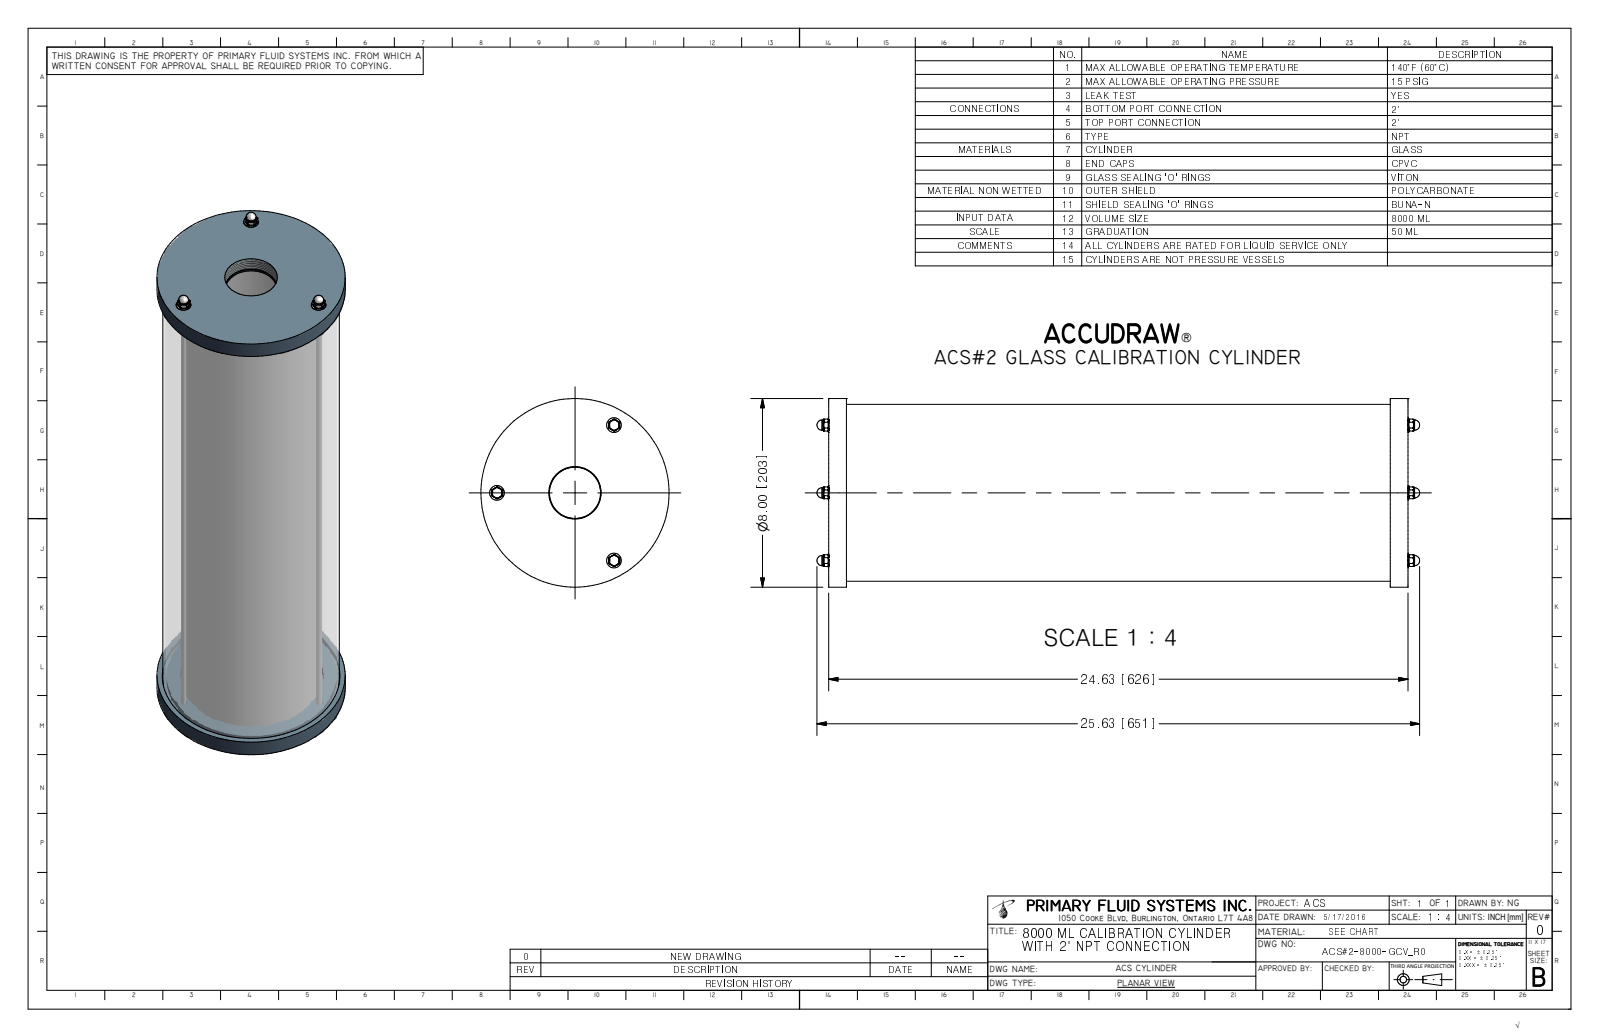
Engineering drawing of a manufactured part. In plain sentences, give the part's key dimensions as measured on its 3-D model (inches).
The part is named "ACS#2-8000-GCV_R0; ACS-3-6000-POLY_R3; ACS-2-8000_R6; ACS-1-8000-A_R0 (+3 more)". Its 3-D file was written by "Autodesk Inventor 2009 (AUTOMOTIVE_DESIGN)". It is 19 solids with 429 faces: 38 planar, 41 cylindrical and 350 other. Overall it measures 25.628 by 8 by 8 inches. Its volume is 217.2 cubic inches and its surface area 2 306 square inches. Round holes: 3 of diameter 0.18, 3 of diameter 0.266, 3 of diameter 0.281, 1 of diameter 5.512, 1 of diameter 6.068, 1 of diameter 7.25, 1 of diameter 7.55. Round bosses or shafts: 3 of diameter 0.625, 3 of diameter 0.25, 1 of diameter 8, 1 of diameter 7.5, 1 of diameter 7.2, 1 of diameter 5.906, 1 of diameter 5.427. The main face-to-face distances are 24.628, 0.75, 23.878, 23.128, 0.375, 24.253, 0.375, 23.503, 0.475, 24.153. The hole center spacings are 3.317, 5.745, 5.745.
